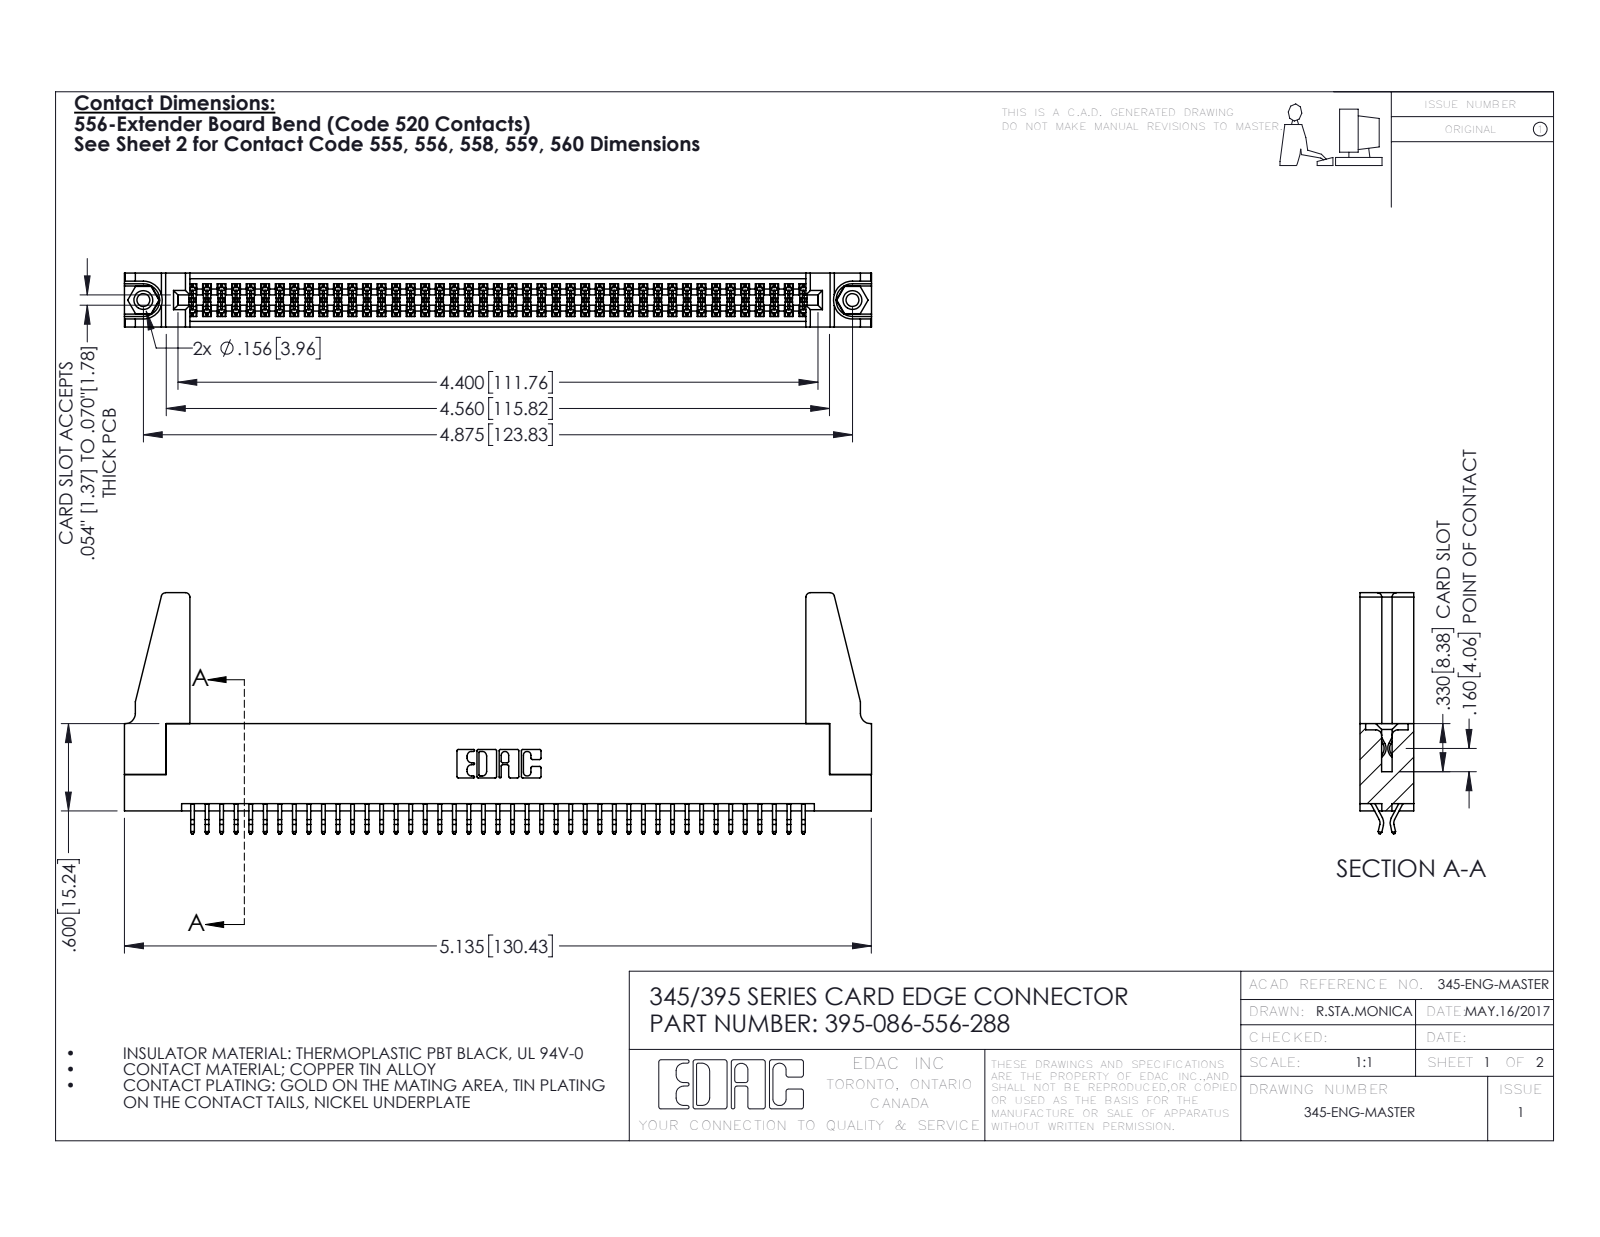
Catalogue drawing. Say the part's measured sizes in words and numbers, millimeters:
The part is named "345-220-078_345-220-088; 345-292-001_556 Tail; 345-250-001_345-250-001-102; 395-086-556-288 (+1 more)". Its 3-D file was written by "SolidWorks 2016 (CONFIG_CONTROL_DESIGN)". It is 91 solids with 5066 faces: 3334 planar, 1716 cylindrical and 16 other. Overall it measures 130.5 by 42.1 by 9.4 millimeters. Its volume is 15 900 cubic millimeters and its surface area 21 810 square millimeters. Round holes: 2 of diameter 2.3, 2 of diameter 3.2, 2 of diameter 4, 1 of diameter 1.6. Round bosses or shafts: 2 of diameter 3.9. Partial cylindrical surfaces (rounded edges, fillets, slot ends): 129 of radius 0.2, 22 of radius 0.3, 8 of radius 0.8, 6 of radius 0.2, 6 of radius 0.8, 3 of radius 0.7, 2 of radius 0.3, 2 of radius 0.4. The main face-to-face distances are 1.8, 7.6, 9.4, 5.1, 0.6, 2.5, 6.9, 5.7, 4.4, 3.8. The hole center spacings are 6.9, 117.8, 123.8.
